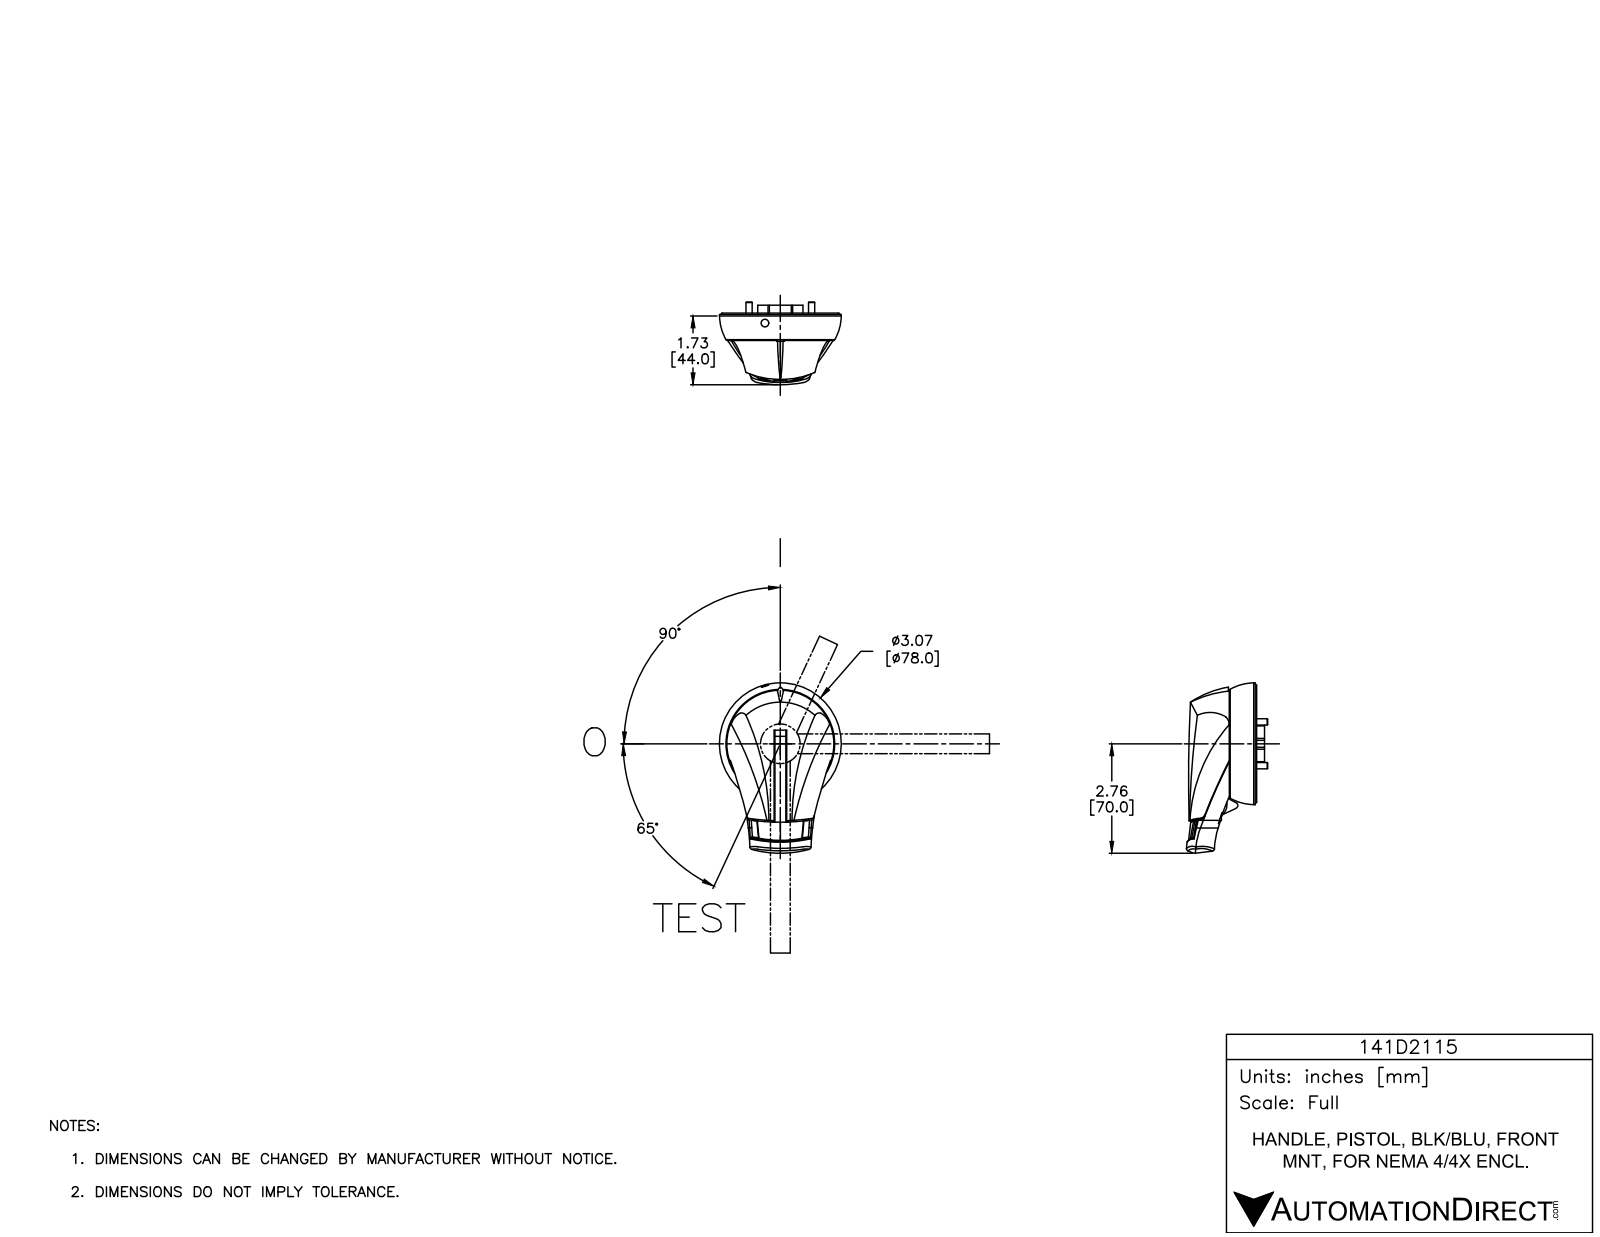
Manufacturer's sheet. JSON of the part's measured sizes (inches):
{"part_name": "141D2115", "step_written_by": "SolidWorks 2015 (AUTOMOTIVE_DESIGN)", "units": "inches", "bodies": {"solids": 8, "faces": 1516, "planar": 810, "cylindrical": 548, "other": 158}, "overall_size": [4.291, 3.07, 2.046], "volume_in3": 7.72, "surface_area_in2": 79.65, "round_holes": [[0.157, 6], [0.339, 4], [0.425, 4], [0.03, 3], [0.169, 2], [0.362, 2], [0.118, 1], [0.189, 1], [2.992, 1]], "round_bosses_or_shafts": [[0.02, 11], [0.335, 4], [0.315, 4], [0.089, 3], [0.069, 3], [0.228, 2], [2.819, 1], [2.701, 1]], "partial_cylinders_radius": [[0.01, 221], [0.015, 20], [0.034, 20], [0.03, 15], [0.039, 4], [0.025, 3], [5.437, 3], [0.079, 2]], "face_to_face_distances": [0.024, 0.701, 0.713, 0.689, 0.035, 0.102, 0.276, 0.173, 0.244, 0.047], "hole_center_spacings": [0.961, 0.309, 0.669, 1.098, 1.102, 1.203, 1.575, 1.881]}
